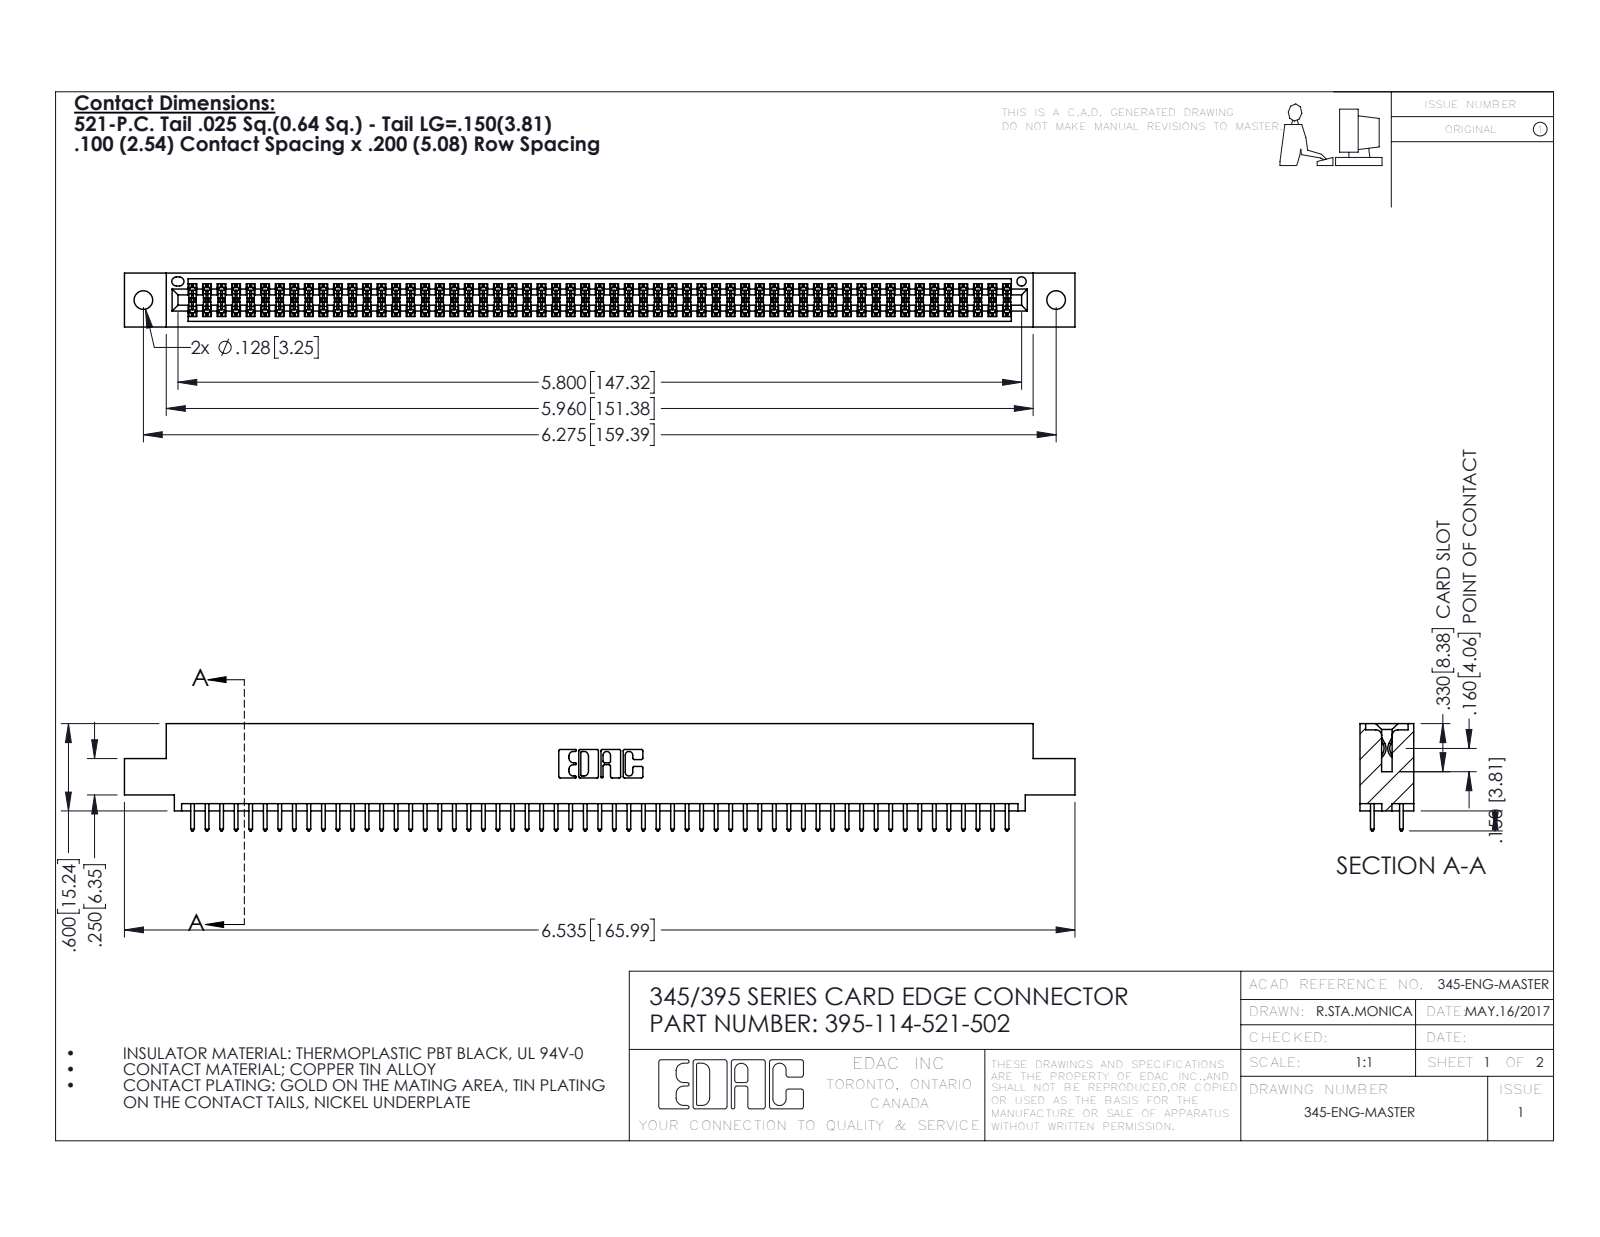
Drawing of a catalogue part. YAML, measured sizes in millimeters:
part_name: "395-114-521-502; 345-292-001_345-293-121; 345 Part_0.110 Offset - 0.128 Dia"
step_written_by: "SolidWorks 2016 (CONFIG_CONTROL_DESIGN)"
units: millimeters
bodies: {solids: 115, faces: 5830, planar: 3846, cylindrical: 1984, other: 0}
overall_size: [166, 18.7, 9.4]
volume: 16100
surface_area: 23620
round_holes:
  - {diameter: 3.3, count: 2}
  - {diameter: 1.6, count: 1}
partial_cylinders:
  - {radius: 0.2, count: 171}
  - {radius: 0.3, count: 114}
  - {radius: 0.3, count: 22}
  - {radius: 0.2, count: 6}
  - {radius: 0.8, count: 6}
  - {radius: 0.7, count: 3}
  - {radius: 0.4, count: 2}
  - {radius: 0.5, count: 2}
face_to_face_distances: [7.6, 1.8, 5.1, 2.5, 6.9, 0.6, 9.4, 5.7, 4.4, 3.8]
hole_center_spacings: [6.9, 153.4, 159.4]
